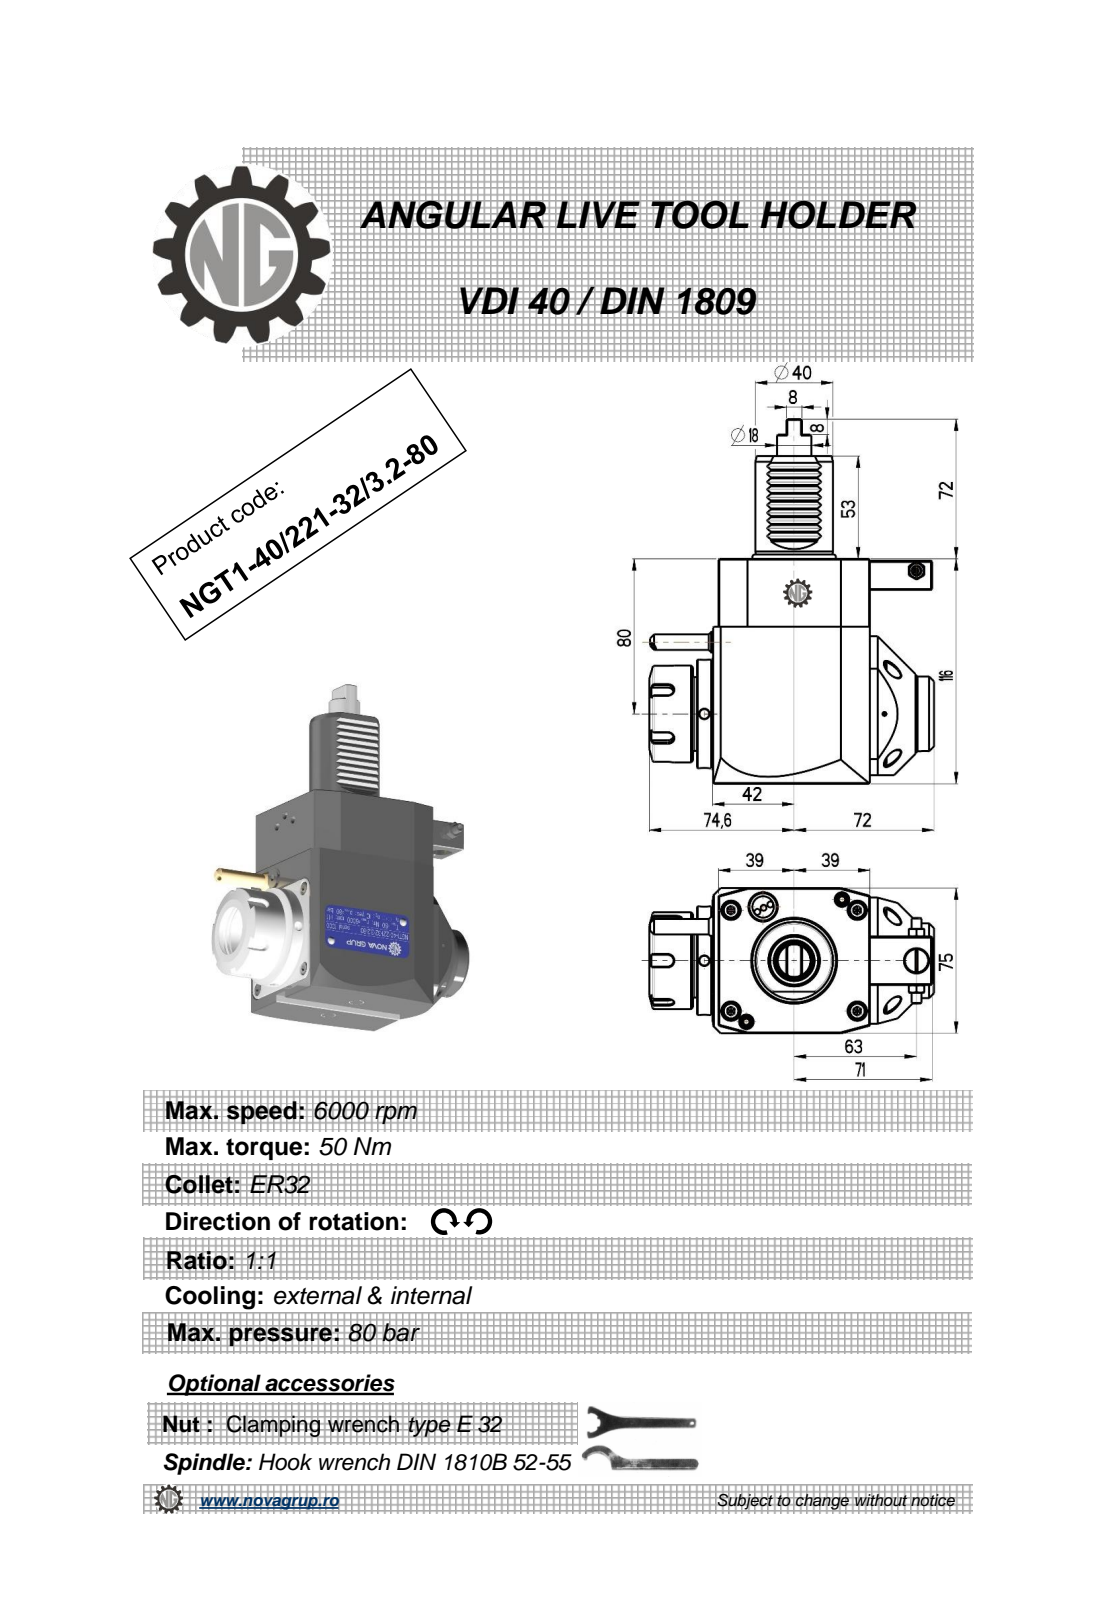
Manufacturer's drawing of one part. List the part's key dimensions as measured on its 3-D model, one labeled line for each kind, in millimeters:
Part name (STEP PRODUCT): NGT1_40_221_32_3_2_80
STEP written by: PRO/ENGINEER BY PARAMETRIC TECHNOLOGY CORPORATION, 2010280 (CONFIG_CONTROL_DESIGN)
Units: millimetres
Bodies: 1 solid, 422 faces (194 planar, 91 cylindrical, 137 other)
Overall size (bounding box): 188 × 146.6 × 75
Volume: 903 020 mm³ · Surface area: 72 659 mm²
Round holes (diameter × count): ⌀5 ×3, ⌀3 ×1, ⌀4.2 ×1, ⌀4.5 ×1, ⌀9.5 ×1, ⌀12 ×1, ⌀27 ×1
Round bosses / shafts (diameter × count): ⌀56 ×1, ⌀50 ×1, ⌀43 ×1, ⌀40 ×1, ⌀38.5 ×1, ⌀17.8 ×1, ⌀11.2 ×1, ⌀8.96 ×1
Partial cylindrical surfaces — rounded edges, fillets, slot ends (radius × count): R0.26 ×12, R0.3 ×10, R0.22 ×6, R3 ×5, R0.8 ×2, R0.5 ×1, R40 ×1
Main face-to-face distances: 75, 116, 81, 78, 3, 2.8, 80.8, 0.5, 8, 11
Hole centre spacings: 39.54, 40.93, 72.45
